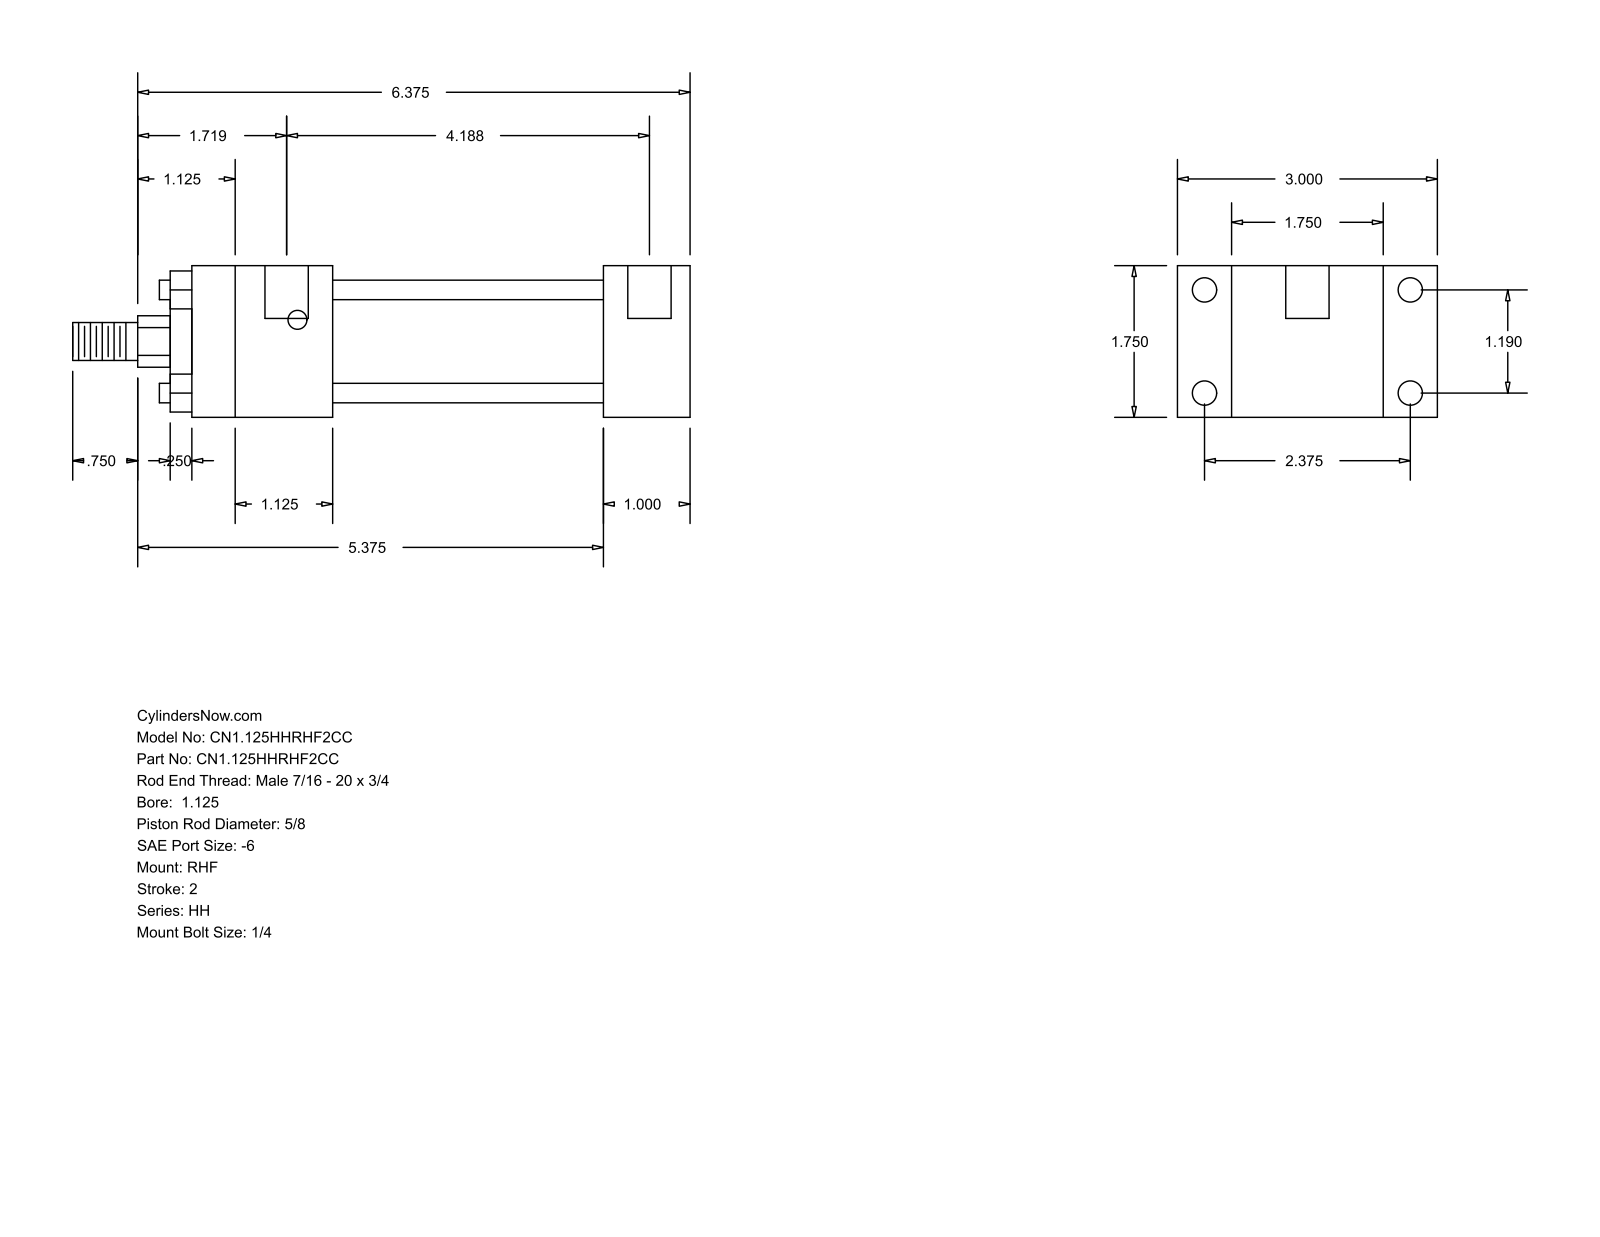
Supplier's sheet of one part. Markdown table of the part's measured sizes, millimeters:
| quantity | value |
| --- | --- |
| part name | HH_RHF__0112_0.625 |
| STEP written by | GSSL Pune (CONFIG_CONTROL_DESIGN) |
| units | millimeters |
| bodies | 0 solids, 88 faces (60 planar, 28 cylindrical, 0 other) |
| overall size | 180.97 × 76.2 × 44.45 |
| round holes (diameter × count) | 5.56 × 4, 7.14 × 4, 12.7 × 2 |
| round bosses / shafts (diameter × count) | 5.71 × 4, 34.92 × 1, 28.57 × 1, 15.88 × 1, 11.11 × 1 |
| partial cylindrical surfaces (radius × count) | 7.54 × 1 |
| main face-to-face distances | 44.46, 15.87, 25.4, 60.33, 76.2, 79.38, 104.78, 41.27, 120.65, 146.05 |
| hole center spacings | 30.22, 60.32, 67.47, 103.19, 3.17, 106.36 |
